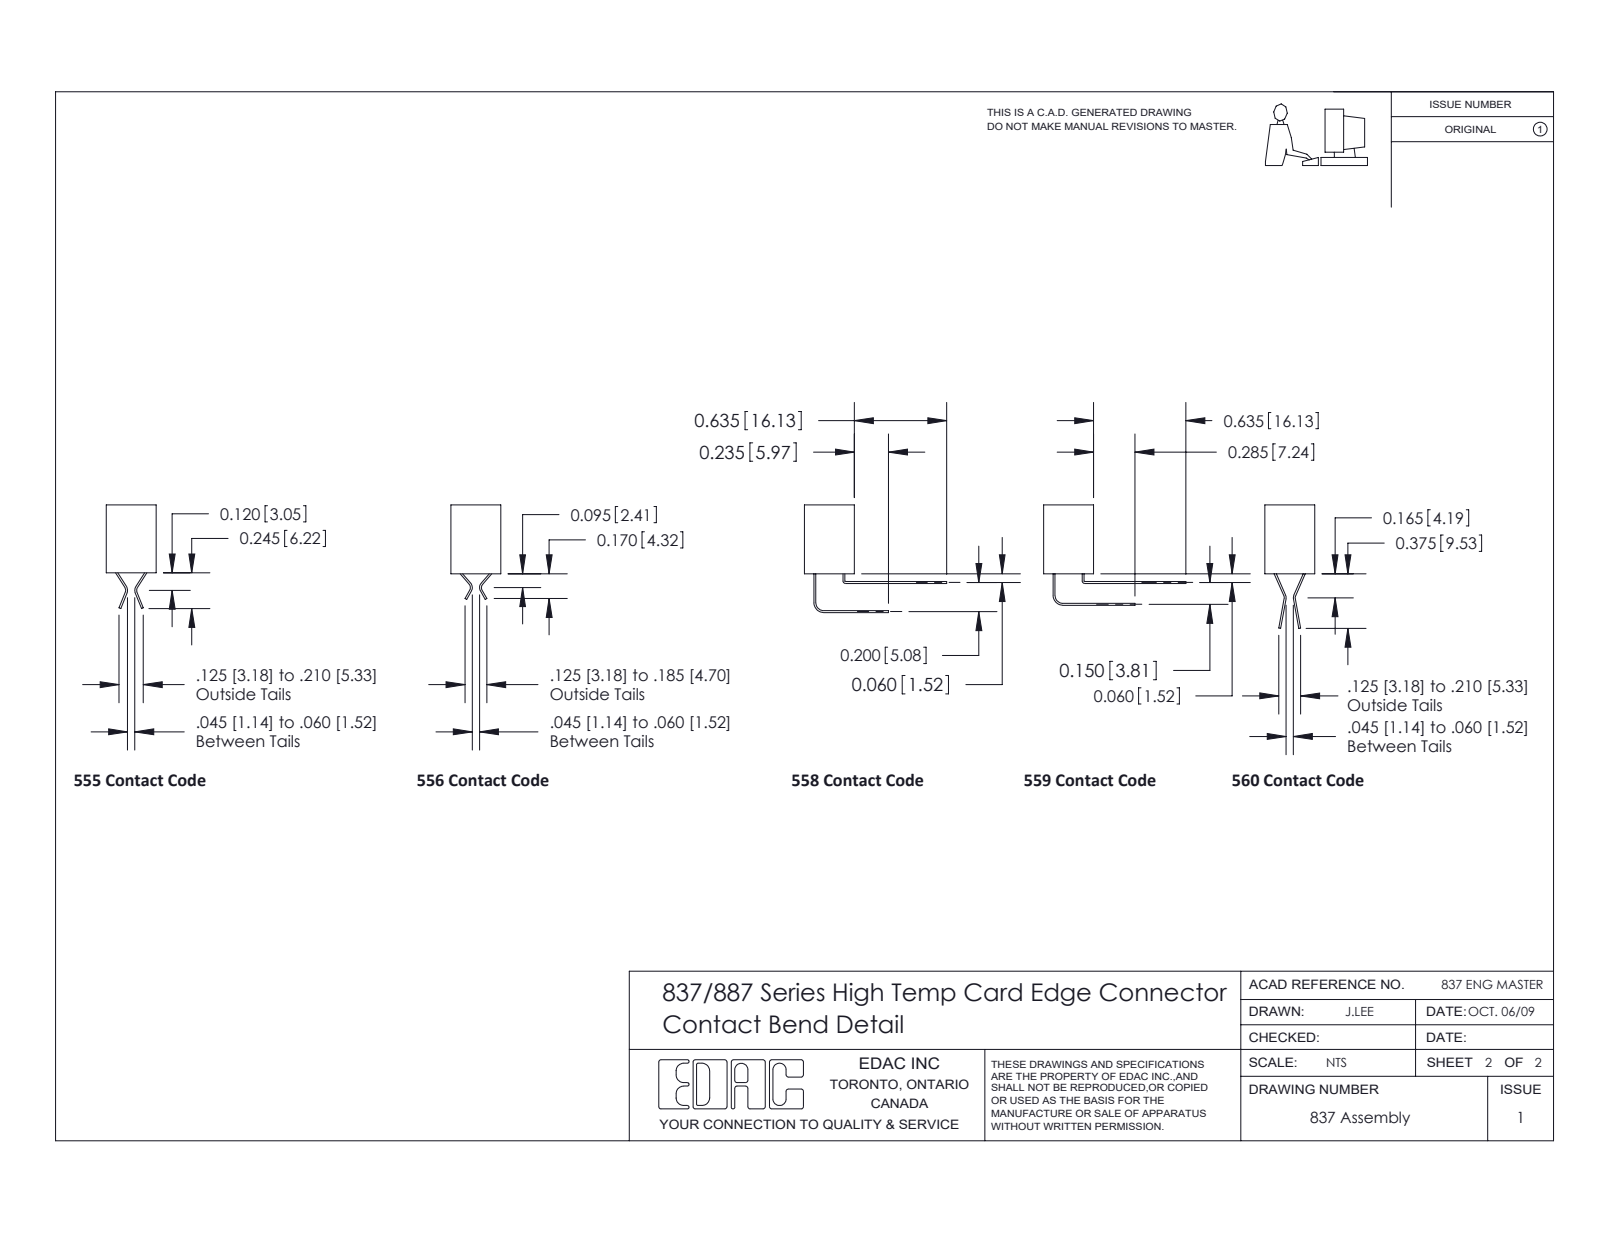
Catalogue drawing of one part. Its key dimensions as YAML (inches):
part_name: "337 Part_Flush Mounting Lugs - 0.156 Dia-TI; 345-250-001_345-250-005-103; 345-292-001_345-293-123; 387-009-523-107"
step_written_by: "SolidWorks 2016 (CONFIG_CONTROL_DESIGN)"
units: inches
bodies: {solids: 12, faces: 732, planar: 516, cylindrical: 200, other: 16}
overall_size: [2.31, 0.99, 0.37]
volume: 0.346
surface_area: 8.871
round_holes:
  - {diameter: 0.098, count: 2}
  - {diameter: 0.125, count: 2}
  - {diameter: 0.156, count: 2}
round_bosses_or_shafts:
  - {diameter: 0.155, count: 2}
partial_cylinders:
  - {radius: 0.01, count: 22}
  - {radius: 0.006, count: 18}
  - {radius: 0.01, count: 18}
  - {radius: 0.007, count: 6}
  - {radius: 0.031, count: 6}
  - {radius: 0.026, count: 3}
  - {radius: 0.014, count: 1}
  - {radius: 0.022, count: 1}
face_to_face_distances: [0.37, 0.072, 0.298, 0.2, 0.149, 0.156, 0.098, 0.272, 0.025, 0.05]
hole_center_spacings: [2]
